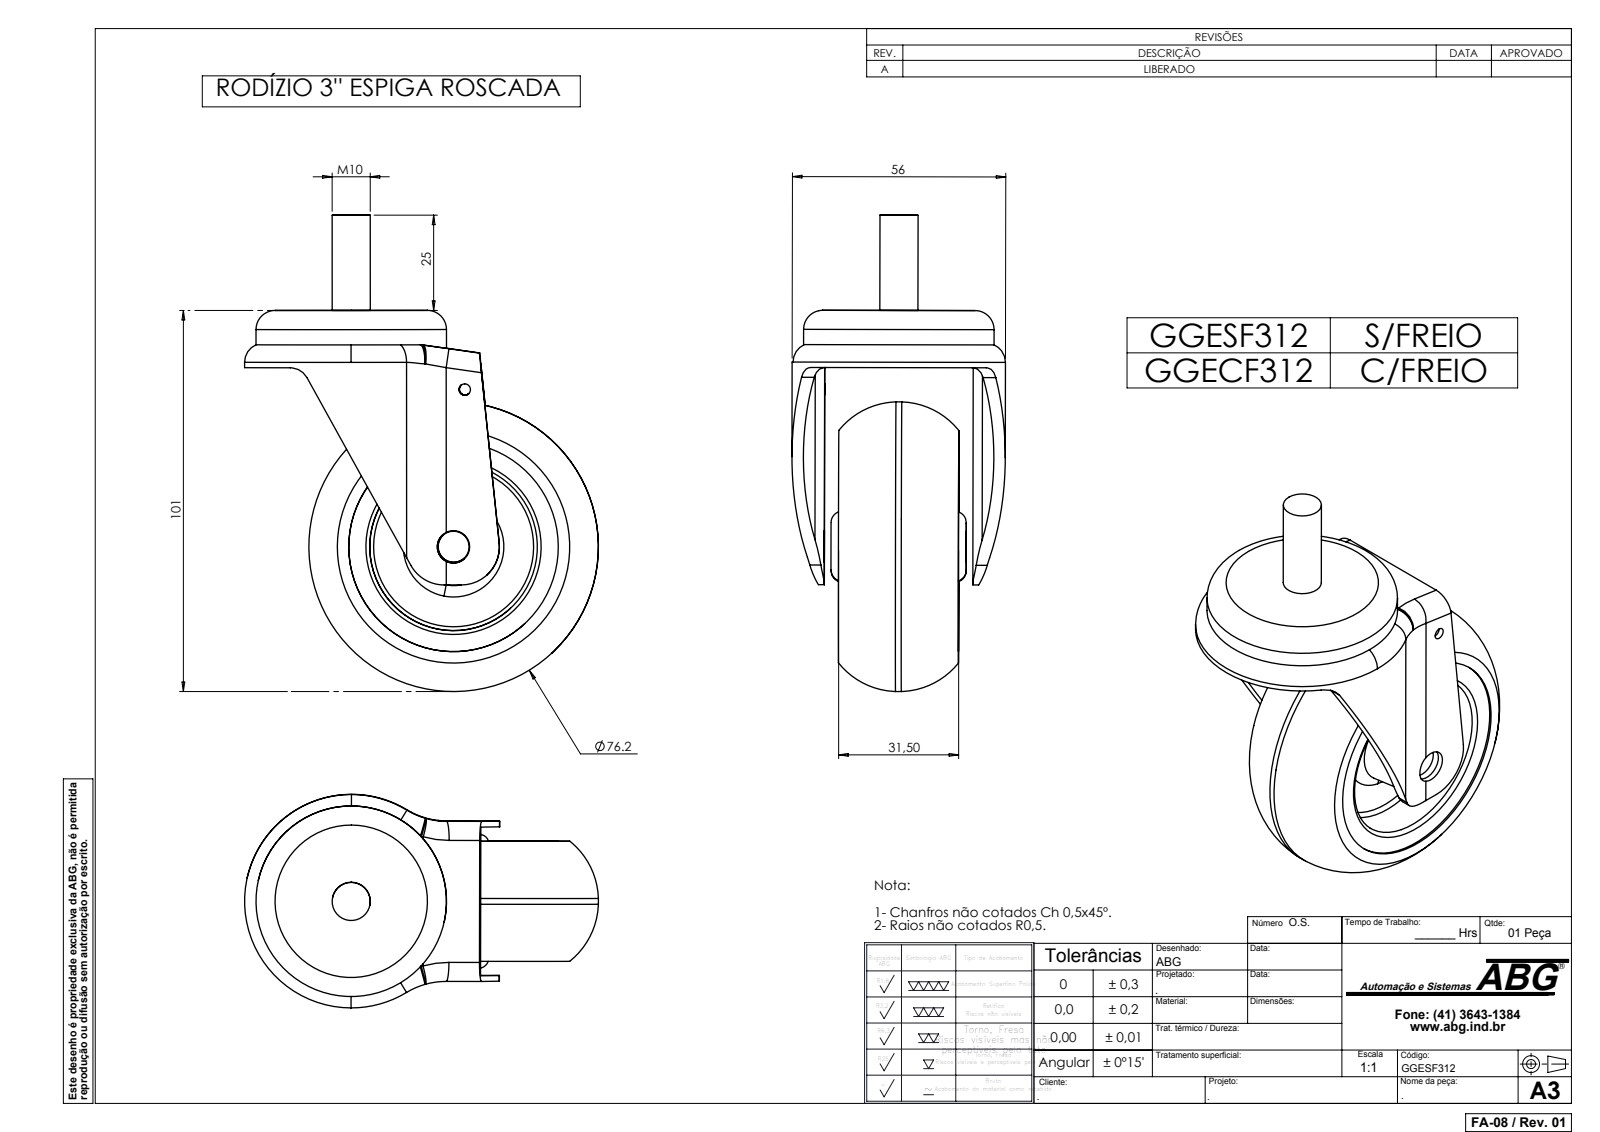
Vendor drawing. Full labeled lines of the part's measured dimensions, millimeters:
Part name (STEP PRODUCT): GGESF312; ROD 3''''''''-2-ESPIGA; ROD 3'''''''' -3
STEP written by: SolidWorks 2007 (CONFIG_CONTROL_DESIGN)
Units: millimetres
Bodies: 2 solids, 103 faces (22 planar, 44 cylindrical, 37 other)
Overall size (bounding box): 125 × 92.88 × 56.04
Volume: 138 812 mm³ · Surface area: 35 624 mm²
Round holes (diameter × count): ⌀3 ×2, ⌀8.5 ×2, ⌀55 ×2, ⌀8.2 ×1, ⌀44 ×1
Round bosses / shafts (diameter × count): ⌀76 ×1, ⌀50 ×1, ⌀10 ×1
Partial cylindrical surfaces — rounded edges, fillets, slot ends (radius × count): R5 ×6, R10 ×4, R20 ×4, R25 ×2, R28 ×1
Main face-to-face distances: 11.5, 19.01, 14.99, 5.24, 36.74, 7.51, 23.24, 15.73, 15.76, 23.27
Hole centre spacings: 41.38, 41.37, 41.39
